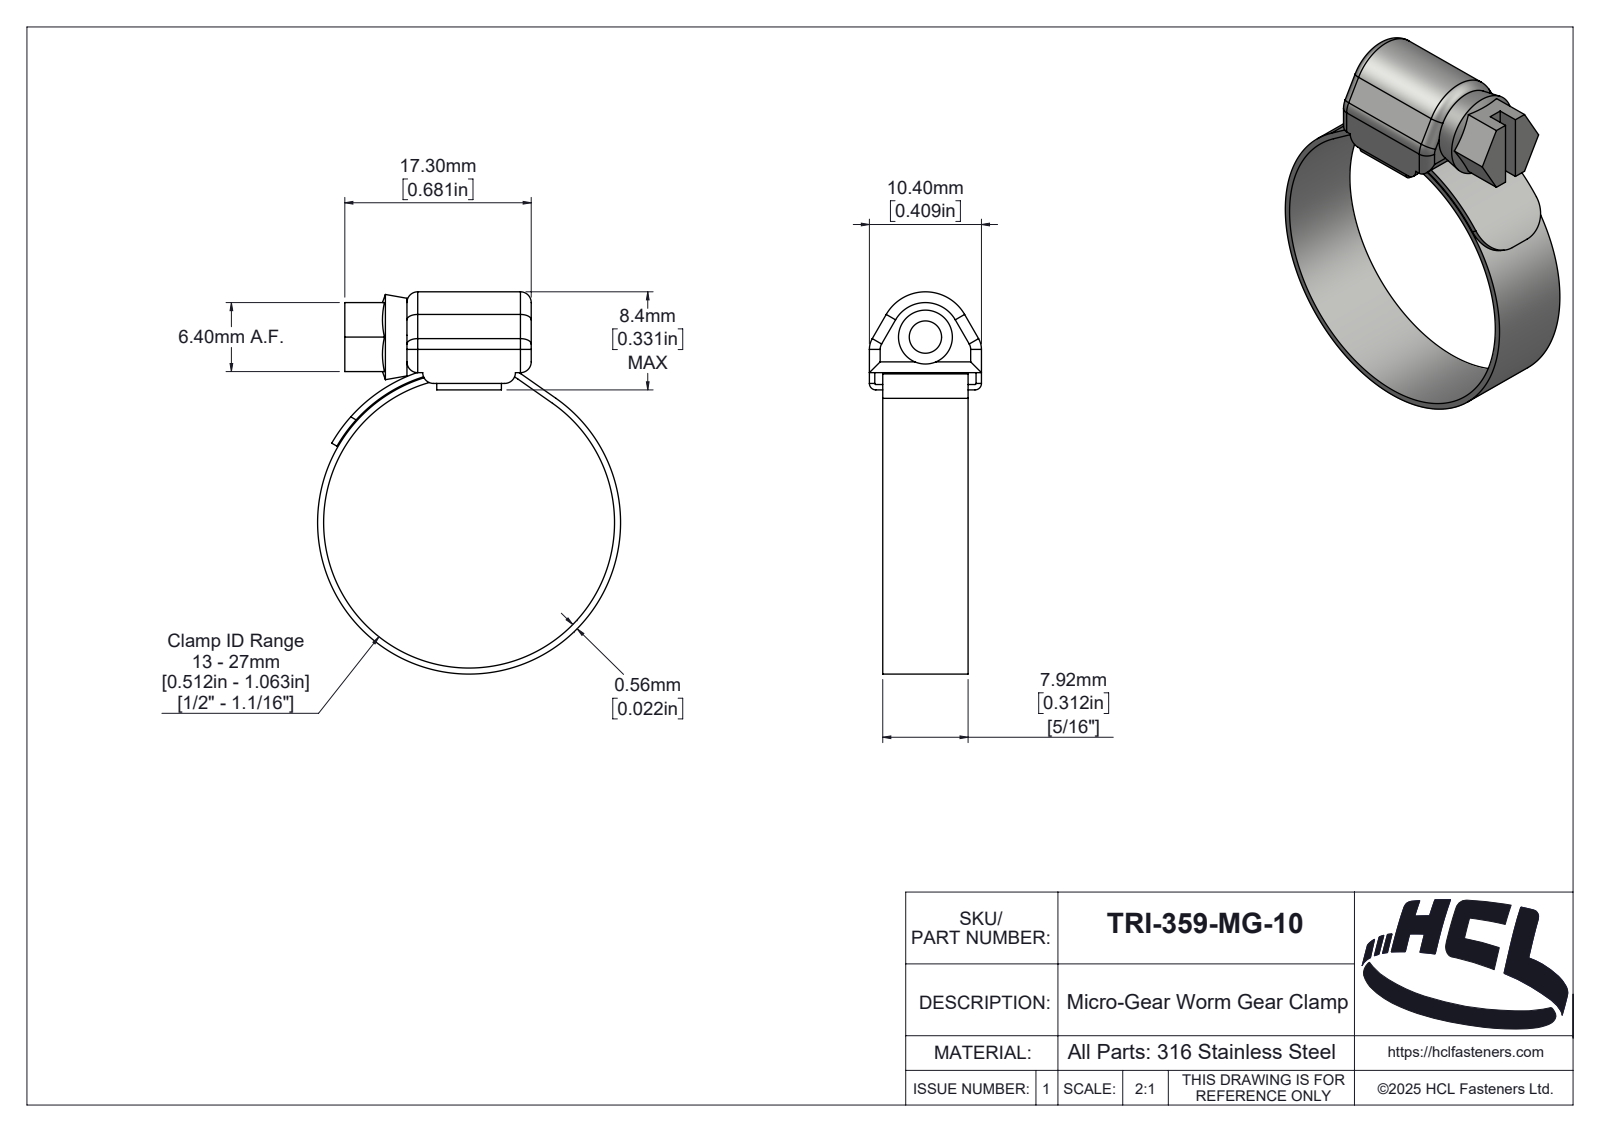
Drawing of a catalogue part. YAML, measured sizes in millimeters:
part_name: "TRI-359-MG-10"
step_written_by: "SolidWorks 2025 (AUTOMOTIVE_DESIGN)"
units: millimeters
bodies: {solids: 3, faces: 186, planar: 38, cylindrical: 87, other: 61}
overall_size: [35.46, 28.12, 10.4]
volume: 1394
surface_area: 2896
round_holes:
  - {diameter: 5, count: 1}
  - {diameter: 27, count: 1}
round_bosses_or_shafts:
  - {diameter: 28.12, count: 1}
partial_cylinders:
  - {radius: 1, count: 12}
  - {radius: 2, count: 3}
  - {radius: 0.1, count: 2}
  - {radius: 0.6, count: 2}
  - {radius: 3, count: 2}
  - {radius: 0.25, count: 1}
  - {radius: 1.01, count: 1}
  - {radius: 1.26, count: 1}
face_to_face_distances: [1.1, 0.5, 1.24, 9.16, 7.92, 1.6, 6.2, 0.56, 10.4, 5.76]
